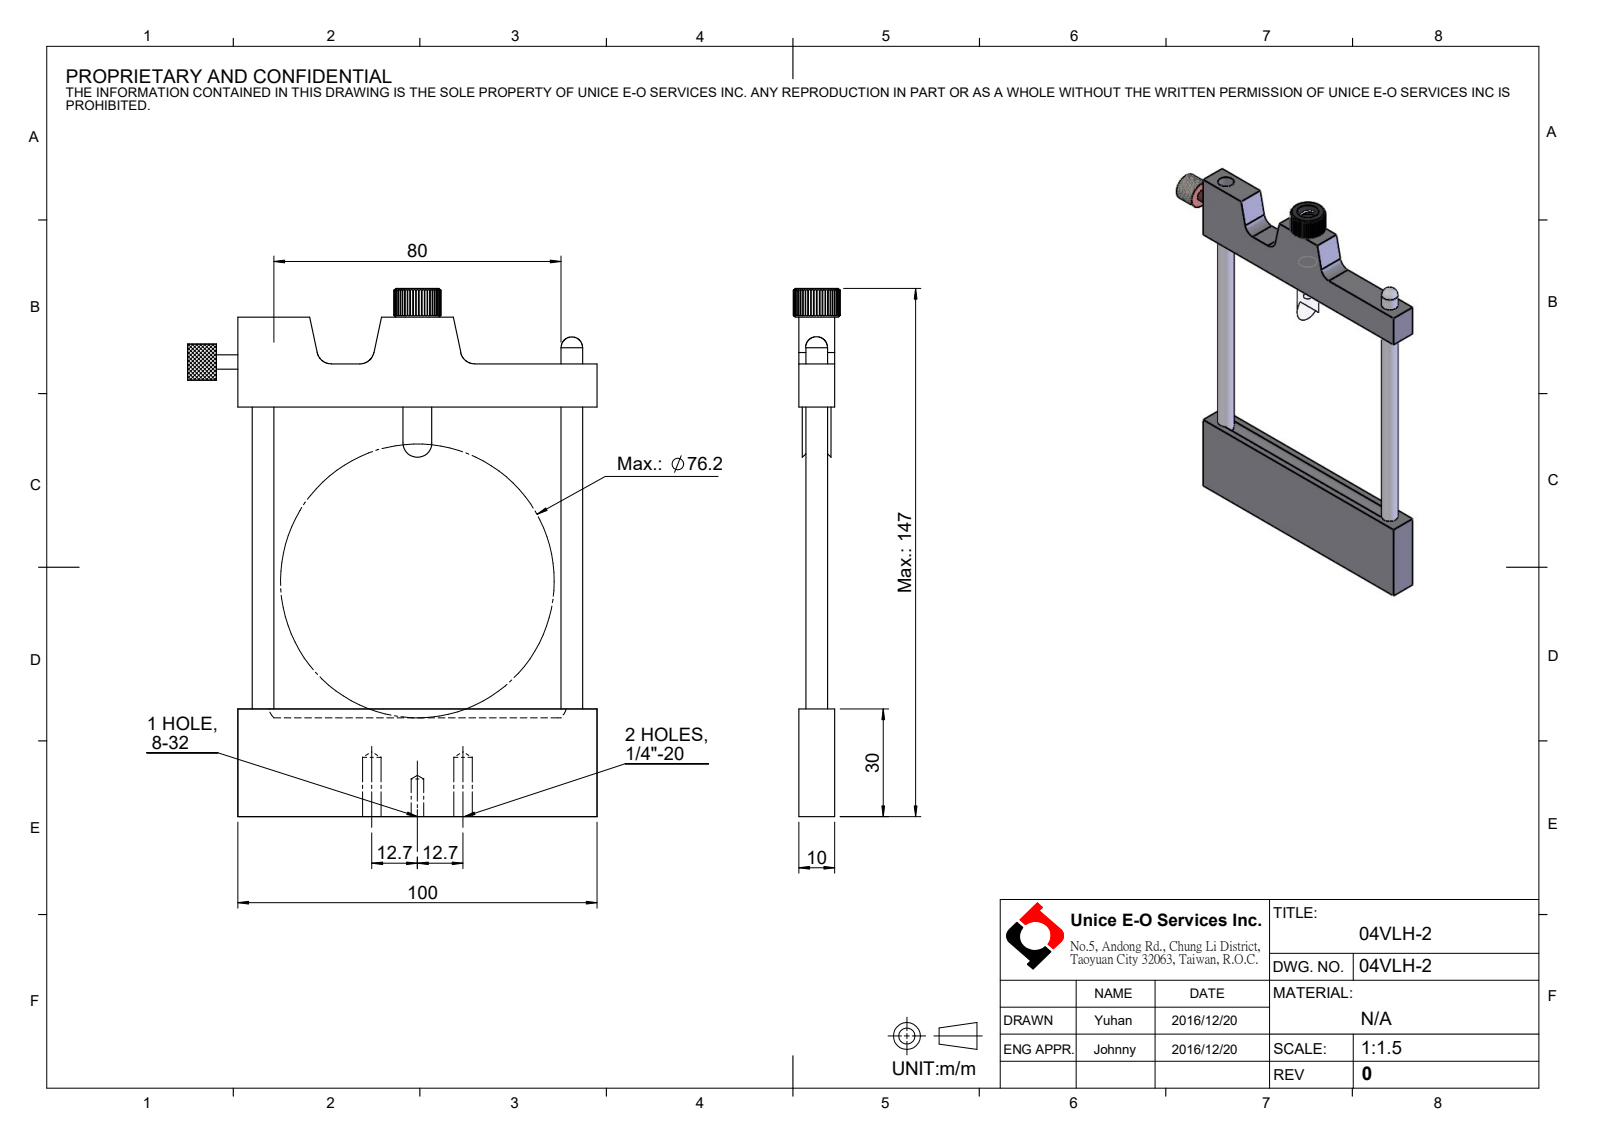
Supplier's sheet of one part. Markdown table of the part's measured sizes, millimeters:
| quantity | value |
| --- | --- |
| part name | 04VLH-2 |
| STEP written by | SolidWorks 2016 (CONFIG_CONTROL_DESIGN) |
| units | millimeters |
| bodies | 8 solids, 209 faces (32 planar, 155 cylindrical, 22 other) |
| overall size | 147 × 114 × 12.98 |
| volume | 52 331 mm³ |
| surface area | 25 263 mm² |
| round holes (diameter × count) | 3.3 × 2, 5.11 × 2, 6 × 2, 3.45 × 1, 4.2 × 1, 8 × 1, 8.5 × 1 |
| round bosses / shafts (diameter × count) | 10 × 1, 4 × 1 |
| partial cylindrical surfaces (radius × count) | 0.4 × 50, 4 × 3, 2.5 × 1, 6.5 × 1 |
| main face-to-face distances | 10, 114, 30, 84, 139, 109, 25, 100, 96, 126 |
| hole center spacings | 12.7, 30.3, 43, 55.7, 25.4, 86 |
